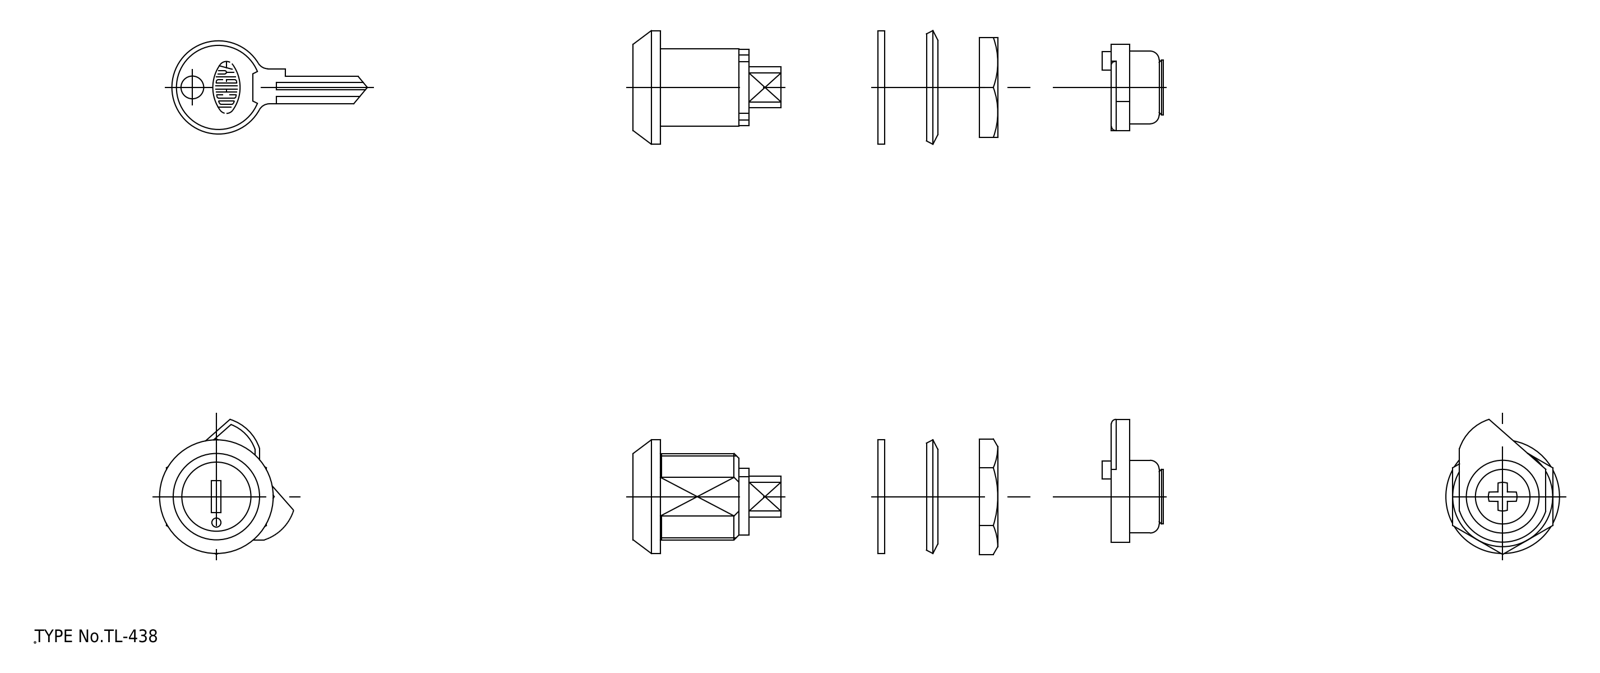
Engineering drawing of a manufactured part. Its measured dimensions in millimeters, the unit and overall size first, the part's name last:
Units: millimetres
Overall size (bounding box): 98.51 × 29.7 × 25
Round holes (diameter × count): ⌀5 ×1, ⌀6 ×1, ⌀12 ×1, ⌀12.6 ×1, ⌀15.5 ×1, ⌀19 ×1, ⌀20 ×1
Round bosses / shafts (diameter × count): ⌀25 ×1, ⌀20.5 ×1, ⌀15.3 ×1, ⌀12.5 ×1, ⌀4 ×1
Partial cylindrical surfaces — rounded edges, fillets, slot ends (radius × count): R1 ×2, R2.5 ×2, R3.15 ×1, R5.5 ×1, R5.75 ×1, R8 ×1, R8.4 ×1, R10 ×1
Main face-to-face distances: 4, 19.5, 1.8, 1.5, 23.5, 22, 17, 18, 6, 7.6
Volume: 12 092 mm³ · Surface area: 10 346 mm²
Bodies: 9 solids, 145 faces (67 planar, 55 cylindrical, 23 other)
Part name (STEP PRODUCT): lock; cam; washer_1; washer_2 (+4 more)
STEP written by: spGate 18.9.1 (****-****-****-****) (AUTOMOTIVE_DESIGN)
